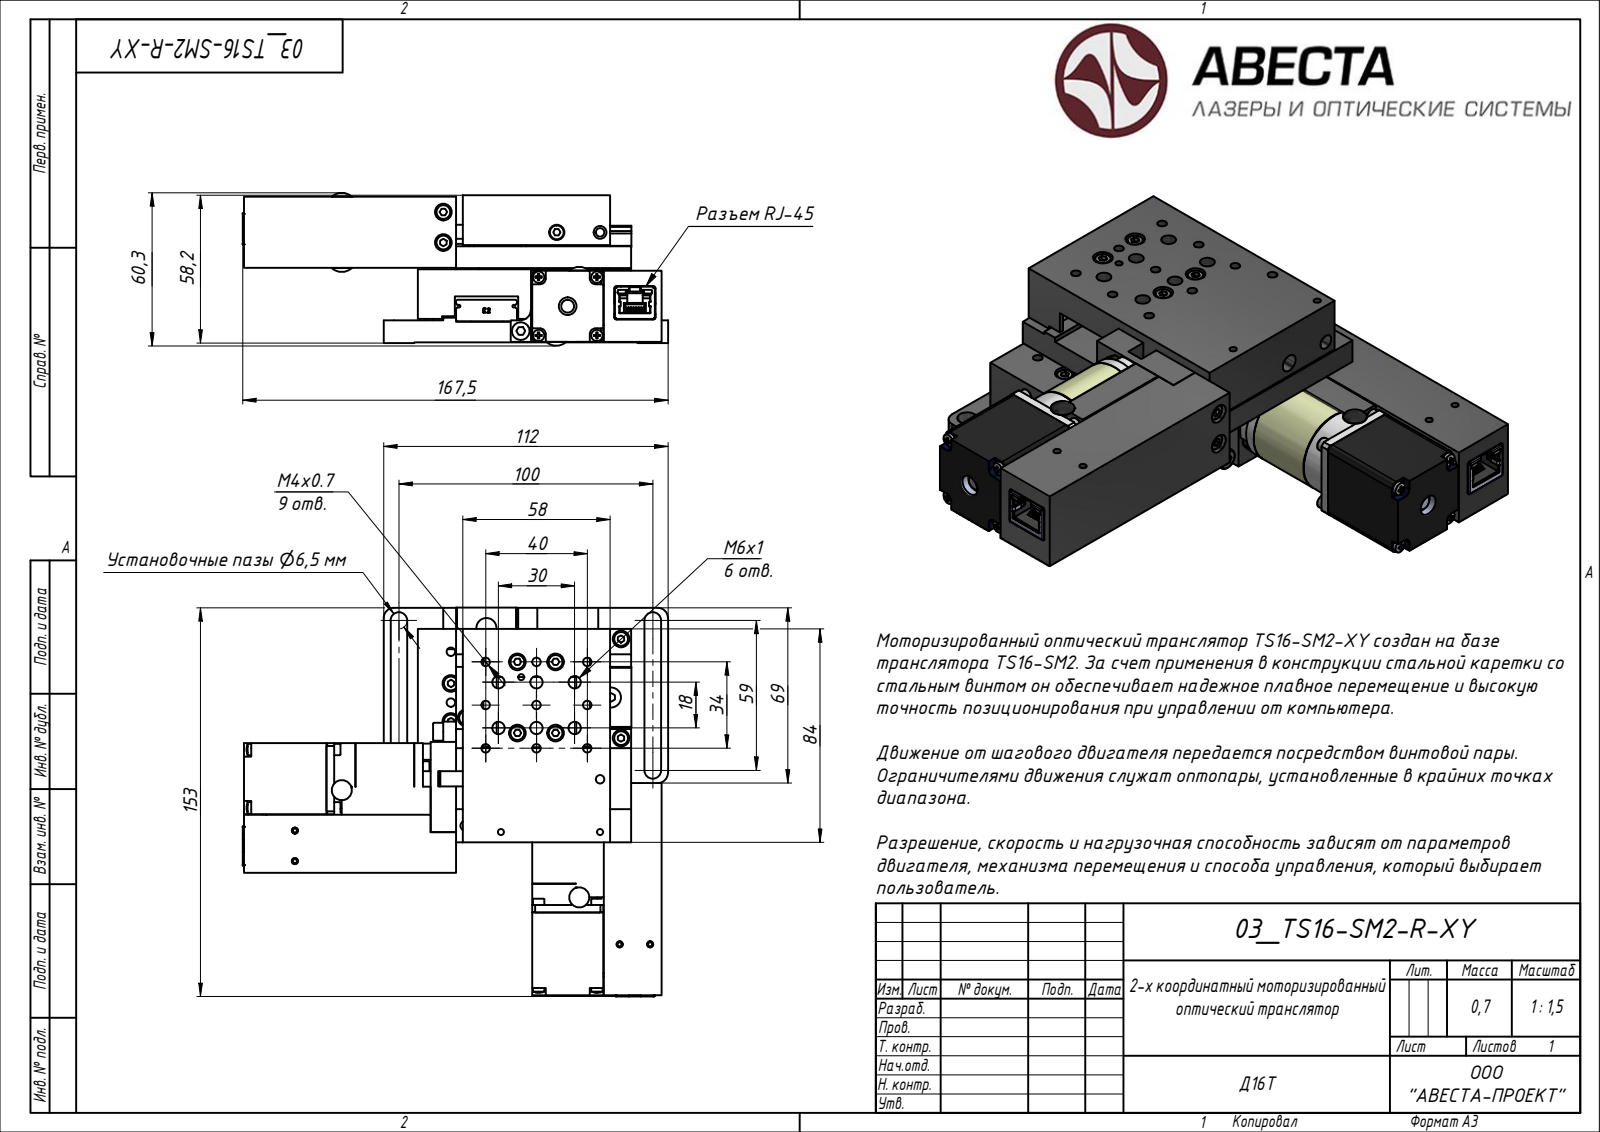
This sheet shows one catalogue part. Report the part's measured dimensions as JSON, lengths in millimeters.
{"step_written_by": "Rhino 7.34 (AUTOMOTIVE_DESIGN)", "units": "millimeters", "bodies": {"solids": 85, "faces": 6493, "planar": 4122, "cylindrical": 1776, "other": 595}, "overall_size": [167.51, 153.26, 60.3], "volume_mm3": 401366, "surface_area_mm2": 166306, "round_holes": [[3.24, 26], [2.5, 24], [0.89, 16], [6.5, 15], [3, 12], [2.46, 9], [0.96, 8], [1.2, 8], [2.9, 8], [5.5, 8], [2.4, 6], [3.4, 5]], "round_bosses_or_shafts": [[4.5, 22], [2, 19], [5.5, 13], [3, 11], [3.4, 10], [2.8, 8], [2.7, 8], [2.46, 8]], "partial_cylinders_radius": [[0.13, 48], [0.38, 46], [0.18, 38], [0.25, 38], [0.15, 34], [0.3, 34], [1, 26], [0.19, 25]], "face_to_face_distances": [29.1, 28, 28.6, 26, 0.6, 2, 20.5, 29.2, 0.5, 5.7], "hole_center_spacings": [19.64, 12, 11, 12.81, 16.26, 16.97, 23, 5.32]}
